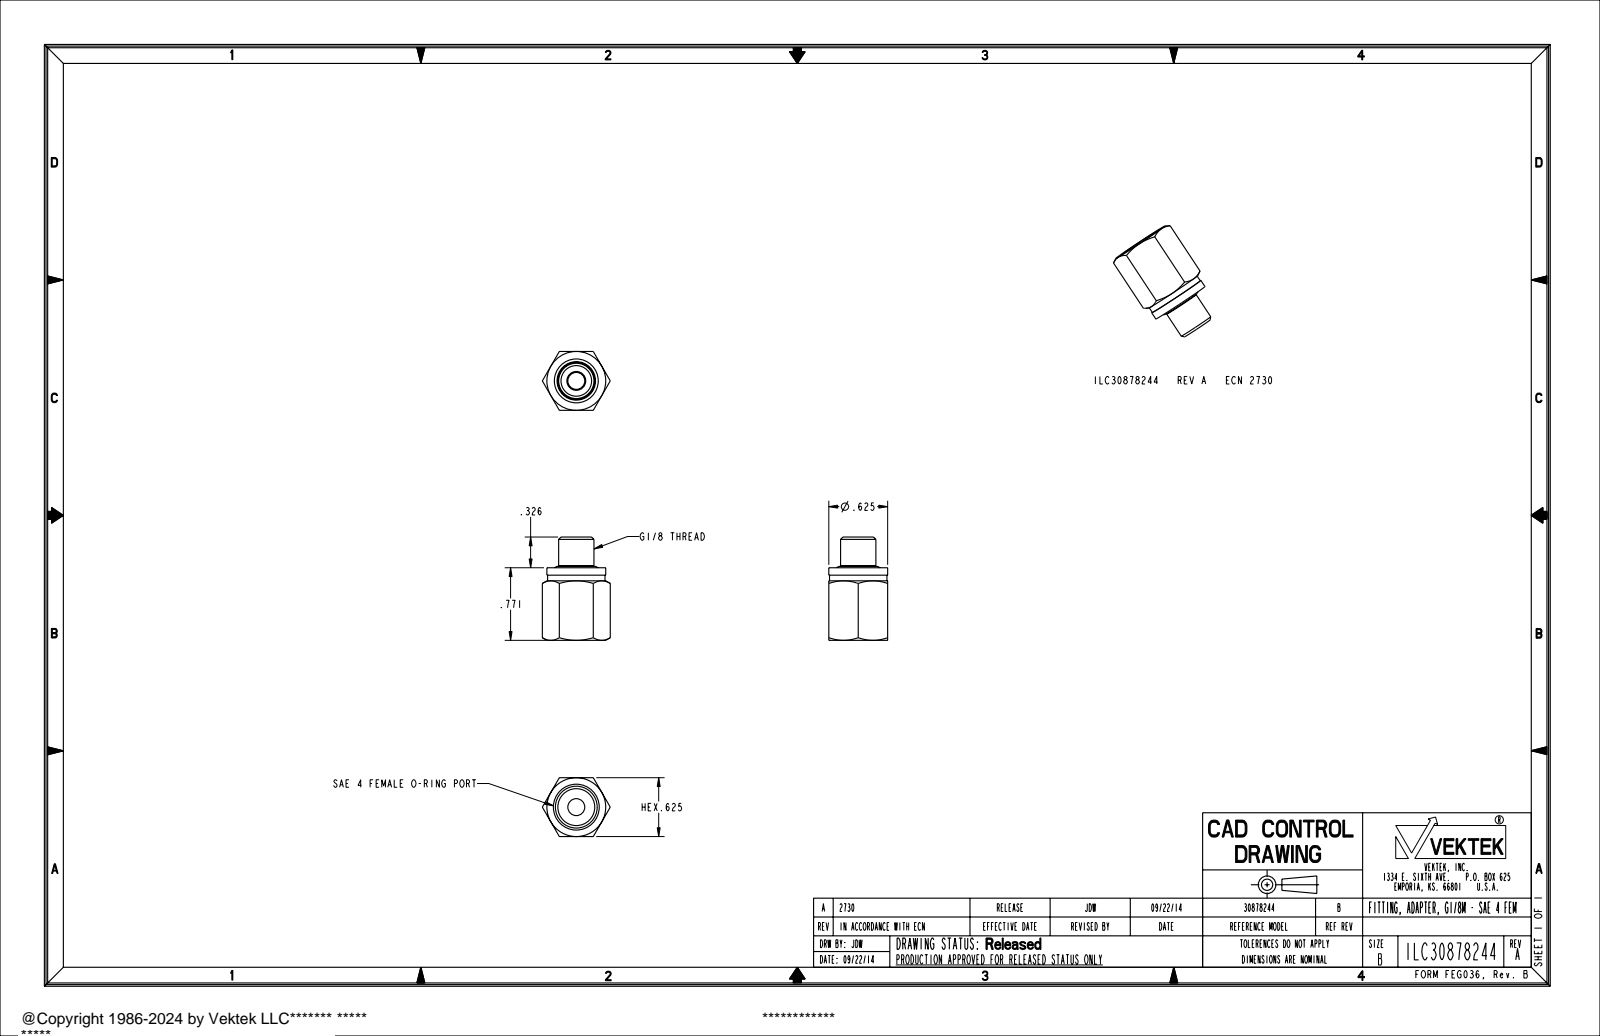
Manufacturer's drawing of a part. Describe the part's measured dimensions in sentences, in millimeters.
The part is named "ILC30878244". Its 3-D file was written by "PRO/ENGINEER BY PARAMETRIC TECHNOLOGY CORPORATION, 2013320 (AUTOMOTIVE_DESIGN)". It is 0 solids with 43 faces: 9 planar, 10 cylindrical and 24 other. Overall it measures 27.9 by 18.3 by 15.9 millimeters. Round holes: 1 of diameter 4.6, 1 of diameter 10. Round bosses or shafts: 1 of diameter 15.9, 1 of diameter 15.5, 1 of diameter 9.5. The main face-to-face distances are 15.9, 19.6, 27.9, 8.3.
